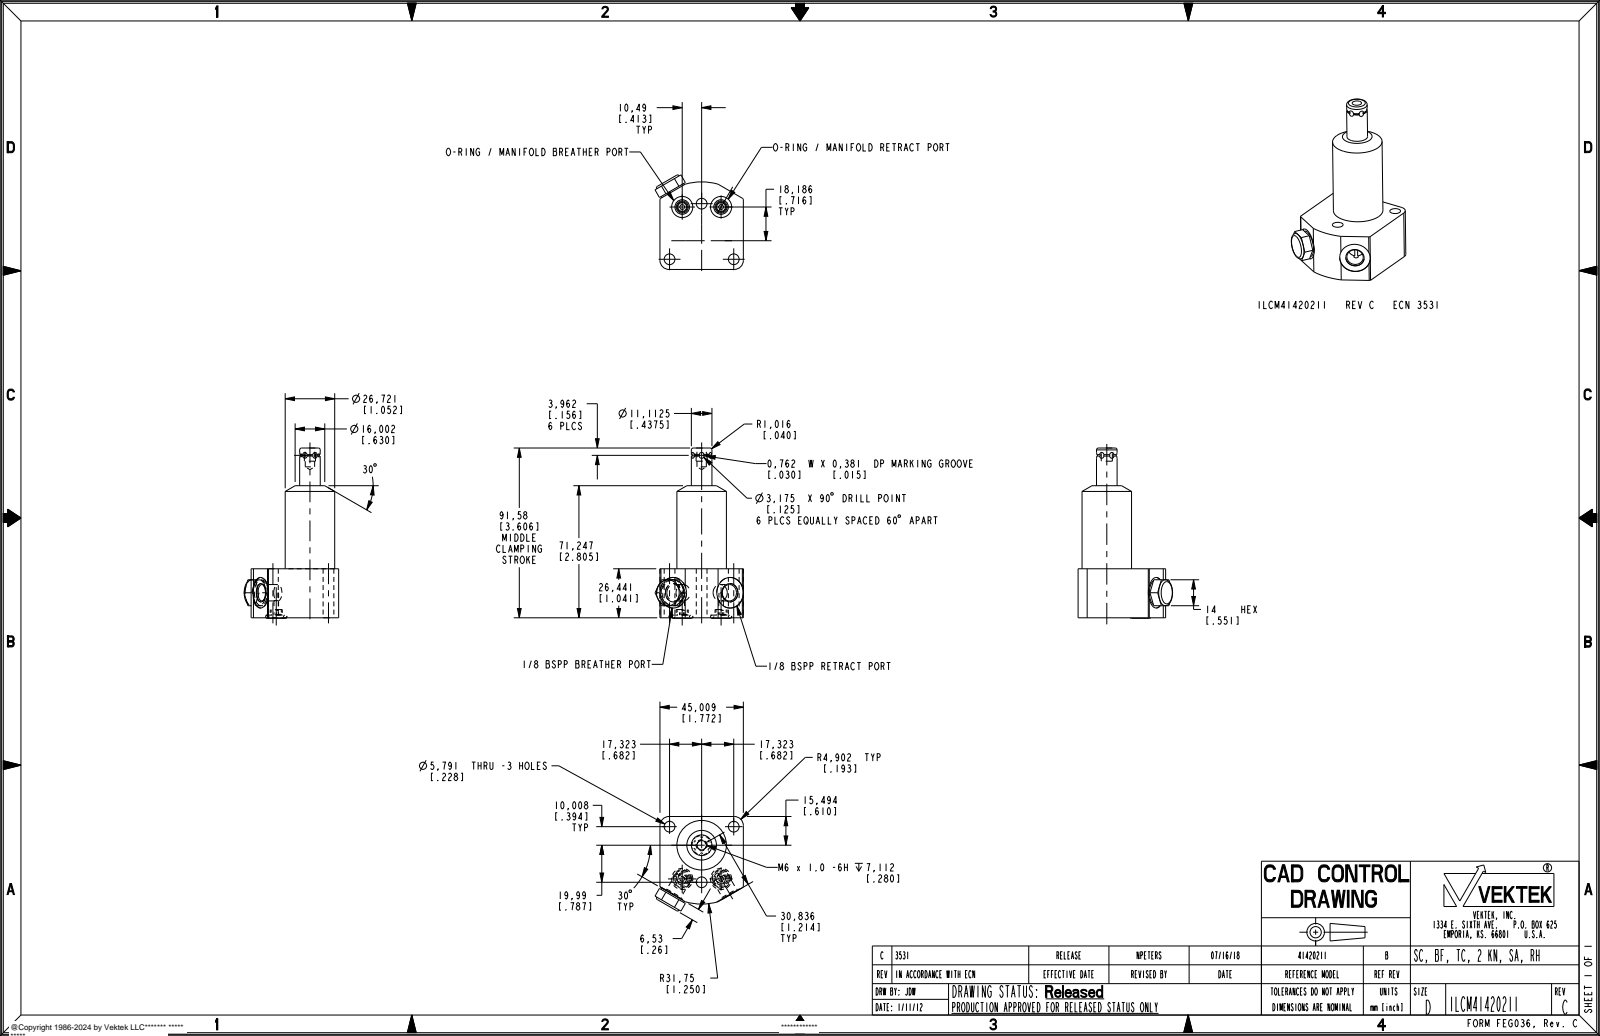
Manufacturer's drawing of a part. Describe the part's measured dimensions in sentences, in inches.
The part is named "ILCM41420211". Its 3-D file was written by "PRO/ENGINEER BY PARAMETRIC TECHNOLOGY CORPORATION, 2013320 (AUTOMOTIVE_DESIGN)". It is 1 solid with 163 faces: 74 planar, 57 cylindrical and 32 other. Overall it measures 3.618 by 2.009 by 1.878 inches. Its volume is 4.612 cubic inches and its surface area 24.82 square inches. Round holes: 3 of diameter 0.228, 2 of diameter 0.098, 2 of diameter 0.256, 2 of diameter 0.348, 2 of diameter 0.39, 2 of diameter 0.449, 2 of diameter 0.65, 1 of diameter 0.199. Round bosses or shafts: 2 of diameter 0.216, 1 of diameter 1.052, 1 of diameter 0.551, 1 of diameter 0.437, 1 of diameter 0.236. Partial cylindrical surfaces (rounded edges, fillets, slot ends): 2 of radius 0.193, 1 of radius 0.204, 1 of radius 1.25. The main face-to-face distances are 1.041, 1.772, 0.057, 0.984, 0.551, 0.257, 0.267, 0.426, 0.416, 2.805. The hole center spacings are 1.364, 0.419, 0.787, 0.827, 1.143, 1.559, 0.787, 0.826.
